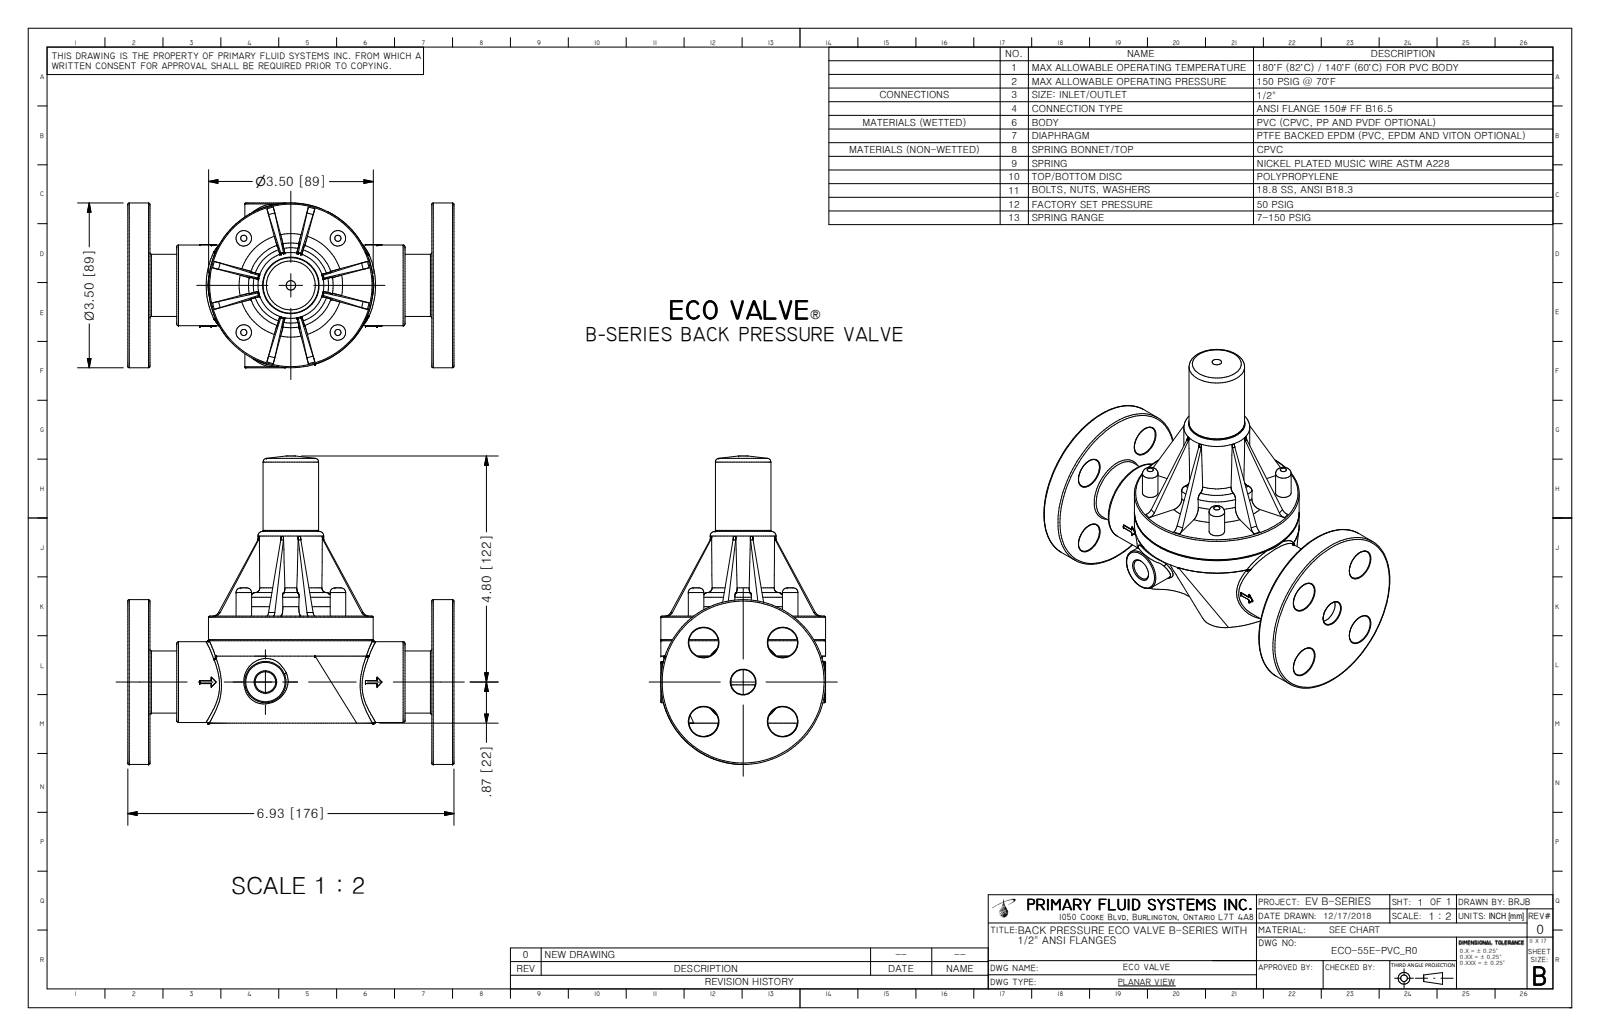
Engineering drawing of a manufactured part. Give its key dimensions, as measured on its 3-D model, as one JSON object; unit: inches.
{"part_name": "ECO-55E-PVC_R0", "step_written_by": "Autodesk Inventor 2009 (AUTOMOTIVE_DESIGN)", "units": "inches", "bodies": {"solids": 1, "faces": 358, "planar": 129, "cylindrical": 82, "other": 147}, "overall_size": [6.93, 6.551, 3.5], "volume_in3": 36.55, "surface_area_in2": 160.6, "round_holes": [[0.63, 6], [0.23, 4], [0.437, 1], [0.526, 1]], "round_bosses_or_shafts": [[0.33, 4], [3.5, 2], [1.8, 1], [1.716, 1], [1.4, 1], [1.32, 1], [1.18, 1], [0.875, 1]], "partial_cylinders_radius": [[0.1, 8], [0.15, 8], [0.05, 4], [0.418, 1], [0.514, 1], [0.669, 1], [0.868, 1], [1.375, 1]], "face_to_face_distances": [0.47, 6.459, 6.93, 5.989, 2.275, 1.04, 5.89, 0.57, 5.42, 1.75], "hole_center_spacings": [1.68, 1.188, 2, 1.187, 1.679, 2.375, 2.375, 2.828]}
